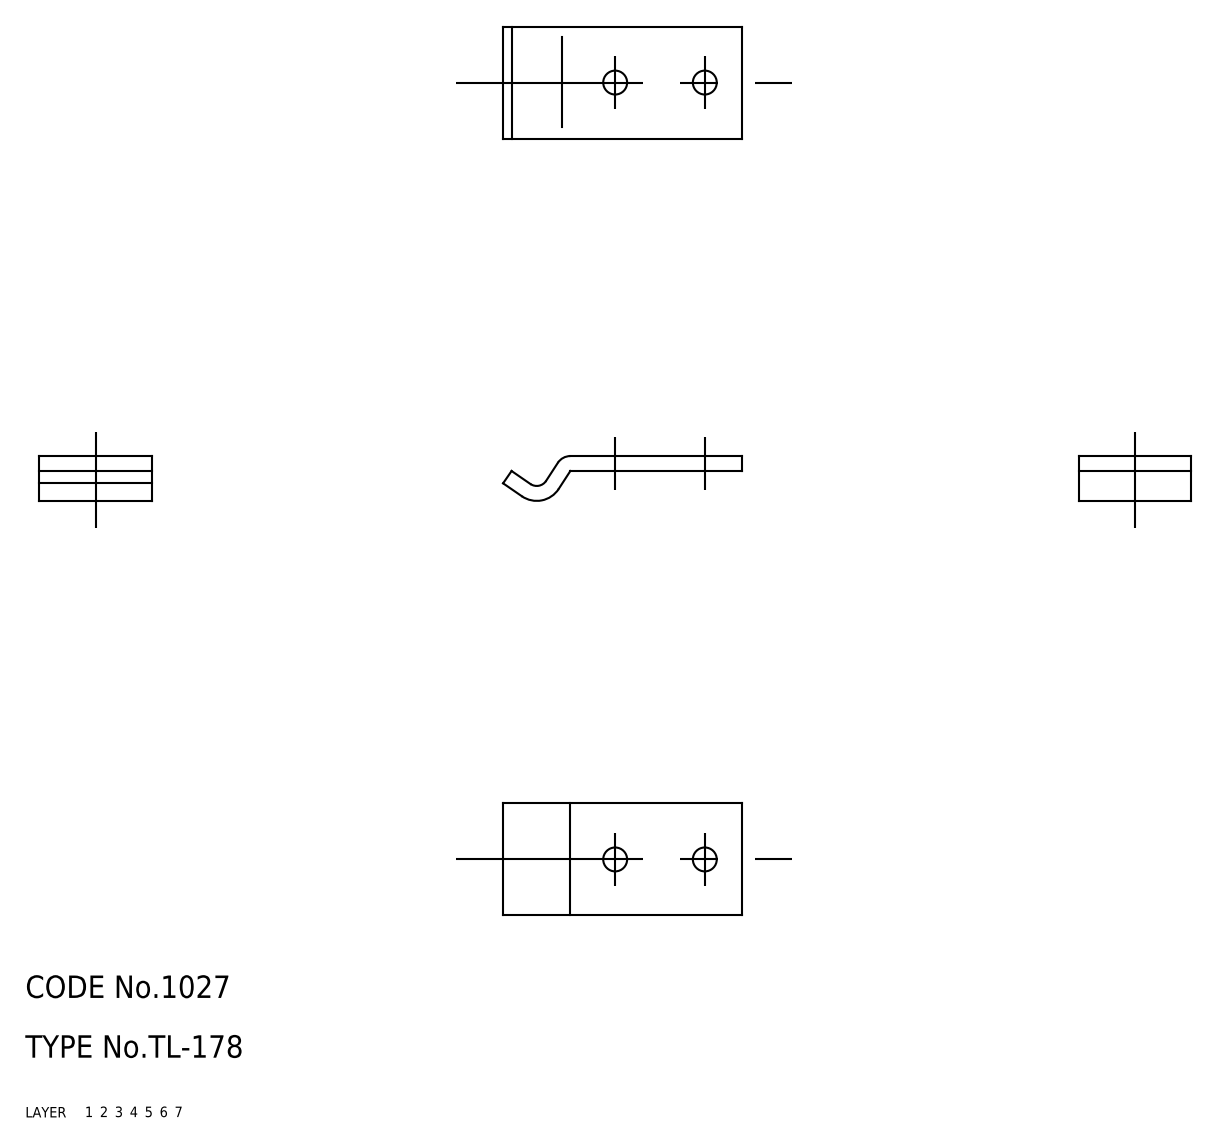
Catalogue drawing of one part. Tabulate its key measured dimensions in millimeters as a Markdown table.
| quantity | value |
| --- | --- |
| part name | keepper |
| STEP written by | CADfix (AUTOMOTIVE_DESIGN) |
| units | millimeters |
| bodies | 1 solid, 17 faces (0 planar, 0 cylindrical, 17 other) |
| overall size | 32 × 15 × 6 |
| volume | 985 mm³ |
| surface area | 1 221 mm² |
